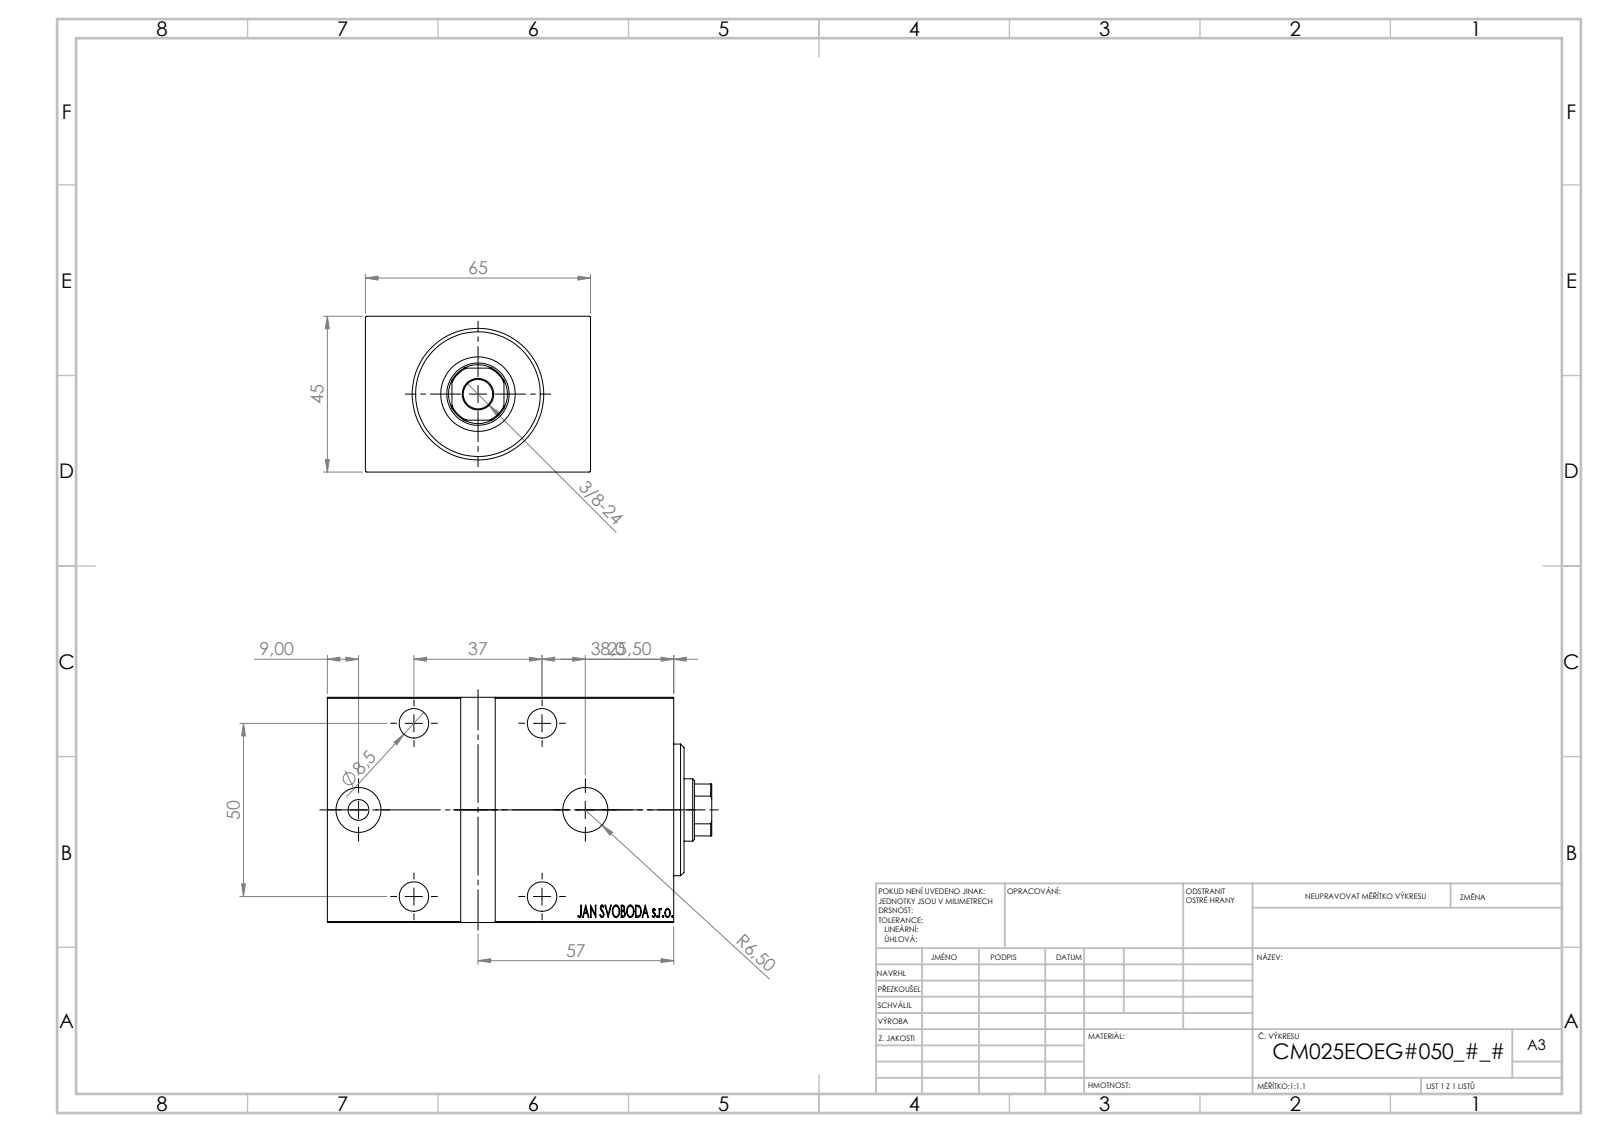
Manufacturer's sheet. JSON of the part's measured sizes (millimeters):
{"part_name": "V450CM_E_Body; V450CM_VC_B; V450CM_E_VCP", "step_written_by": "SolidWorks 2019 (CONFIG_CONTROL_DESIGN)", "units": "millimeters", "bodies": {"solids": 3, "faces": 849, "planar": 409, "cylindrical": 46, "other": 394}, "overall_size": [111, 65, 45], "volume_mm3": 271026, "surface_area_mm2": 53543, "round_holes": [[8.5, 5], [13.5, 4], [13, 2], [18, 1], [21.5, 1], [25, 1], [35, 1]], "round_bosses_or_shafts": [[38, 1], [27, 1], [6, 1]], "partial_cylinders_radius": [[8.5, 1]], "face_to_face_distances": [45, 65, 100, 6, 94, 5, 95, 89, 8, 3], "hole_center_spacings": [27.95, 29.68, 37, 50, 55.45, 58.6, 62.2, 65.5]}
